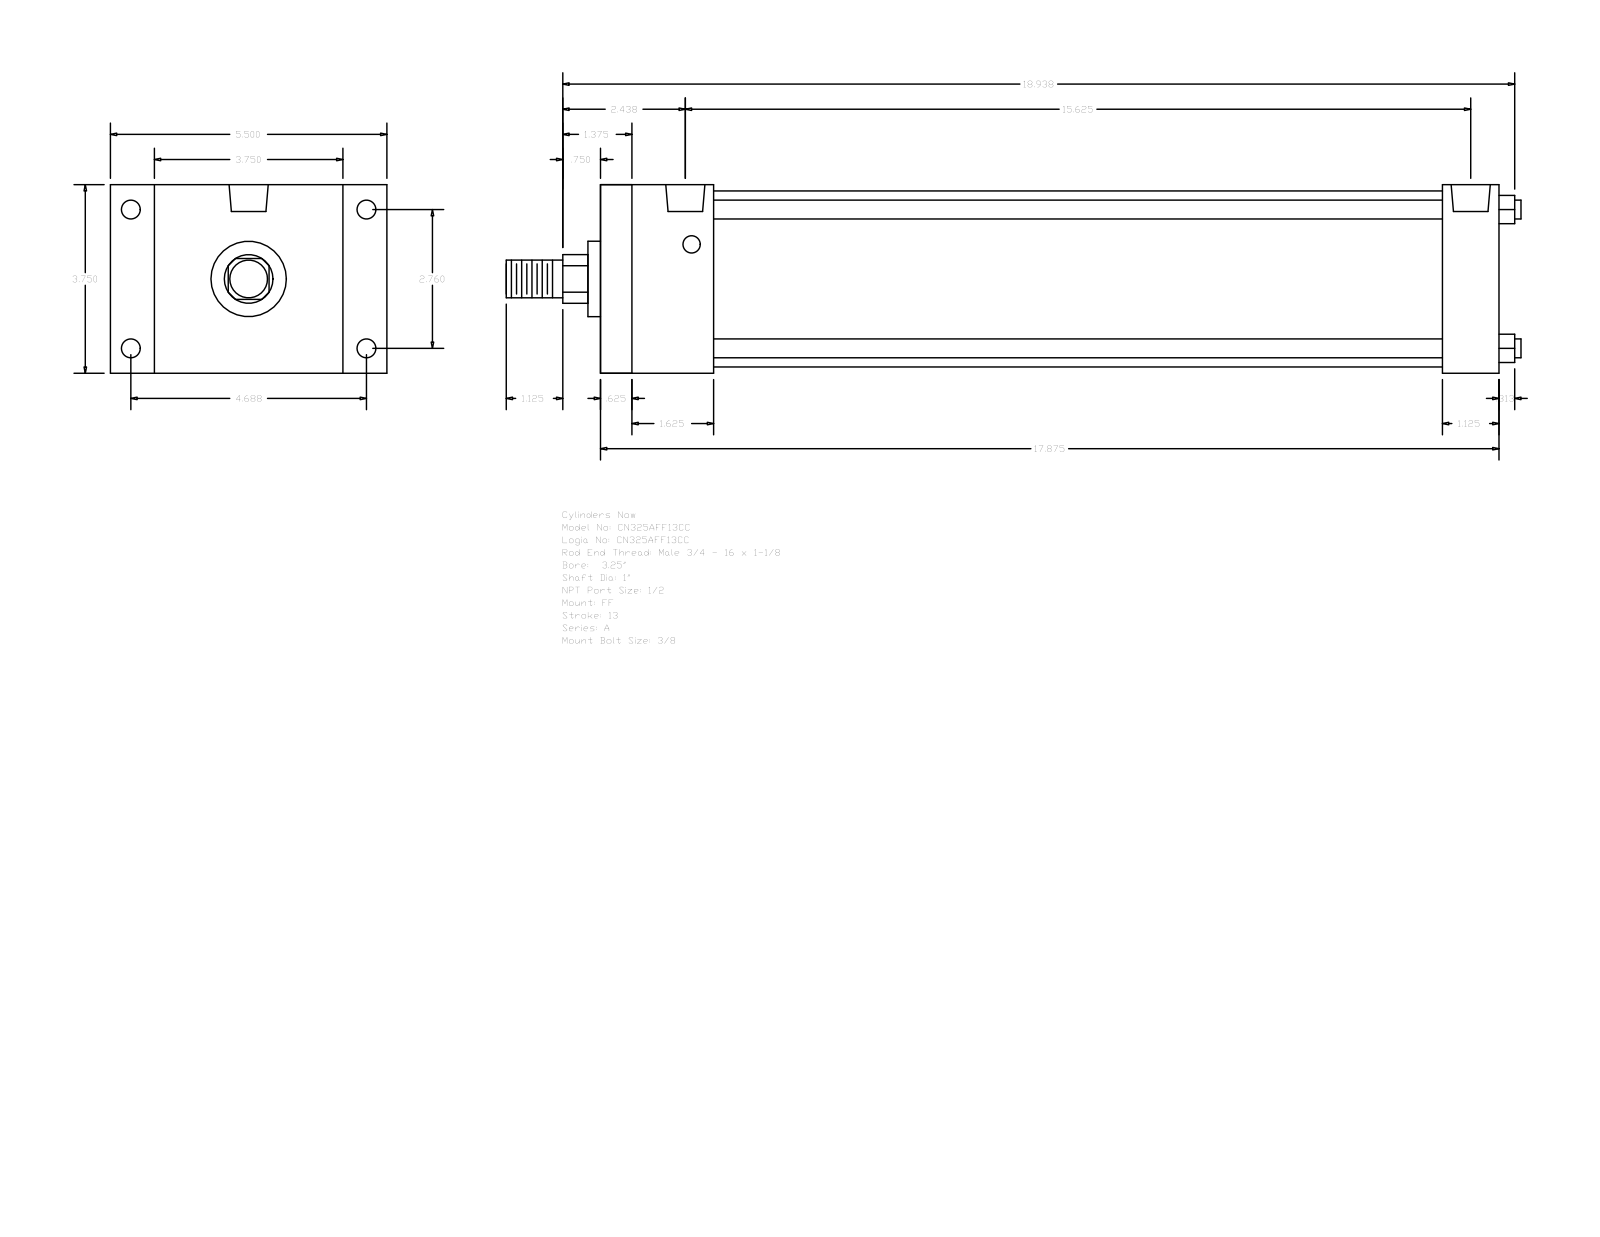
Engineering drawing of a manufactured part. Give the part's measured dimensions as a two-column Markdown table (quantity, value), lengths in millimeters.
| quantity | value |
| --- | --- |
| part name | A_FF__0325_1 |
| STEP written by | GSSL Pune (CONFIG_CONTROL_DESIGN) |
| units | millimeters |
| bodies | 0 solids, 92 faces (64 planar, 28 cylindrical, 0 other) |
| overall size | 512.76 × 139.7 × 95.25 |
| round holes (diameter × count) | 8.73 × 4, 9.53 × 4, 19.77 × 2 |
| round bosses / shafts (diameter × count) | 9.53 × 4, 88.9 × 1, 38.1 × 1, 25.4 × 1, 19.05 × 1 |
| partial cylindrical surfaces (radius × count) | 12.29 × 1 |
| main face-to-face distances | 95.24, 454.02, 15.87, 438.15, 22.23, 117.47, 28.57, 57.15, 425.45, 41.28 |
| hole center spacings | 3.18, 70.1, 119.06, 138.16, 390.52, 393.7, 396.88 |
